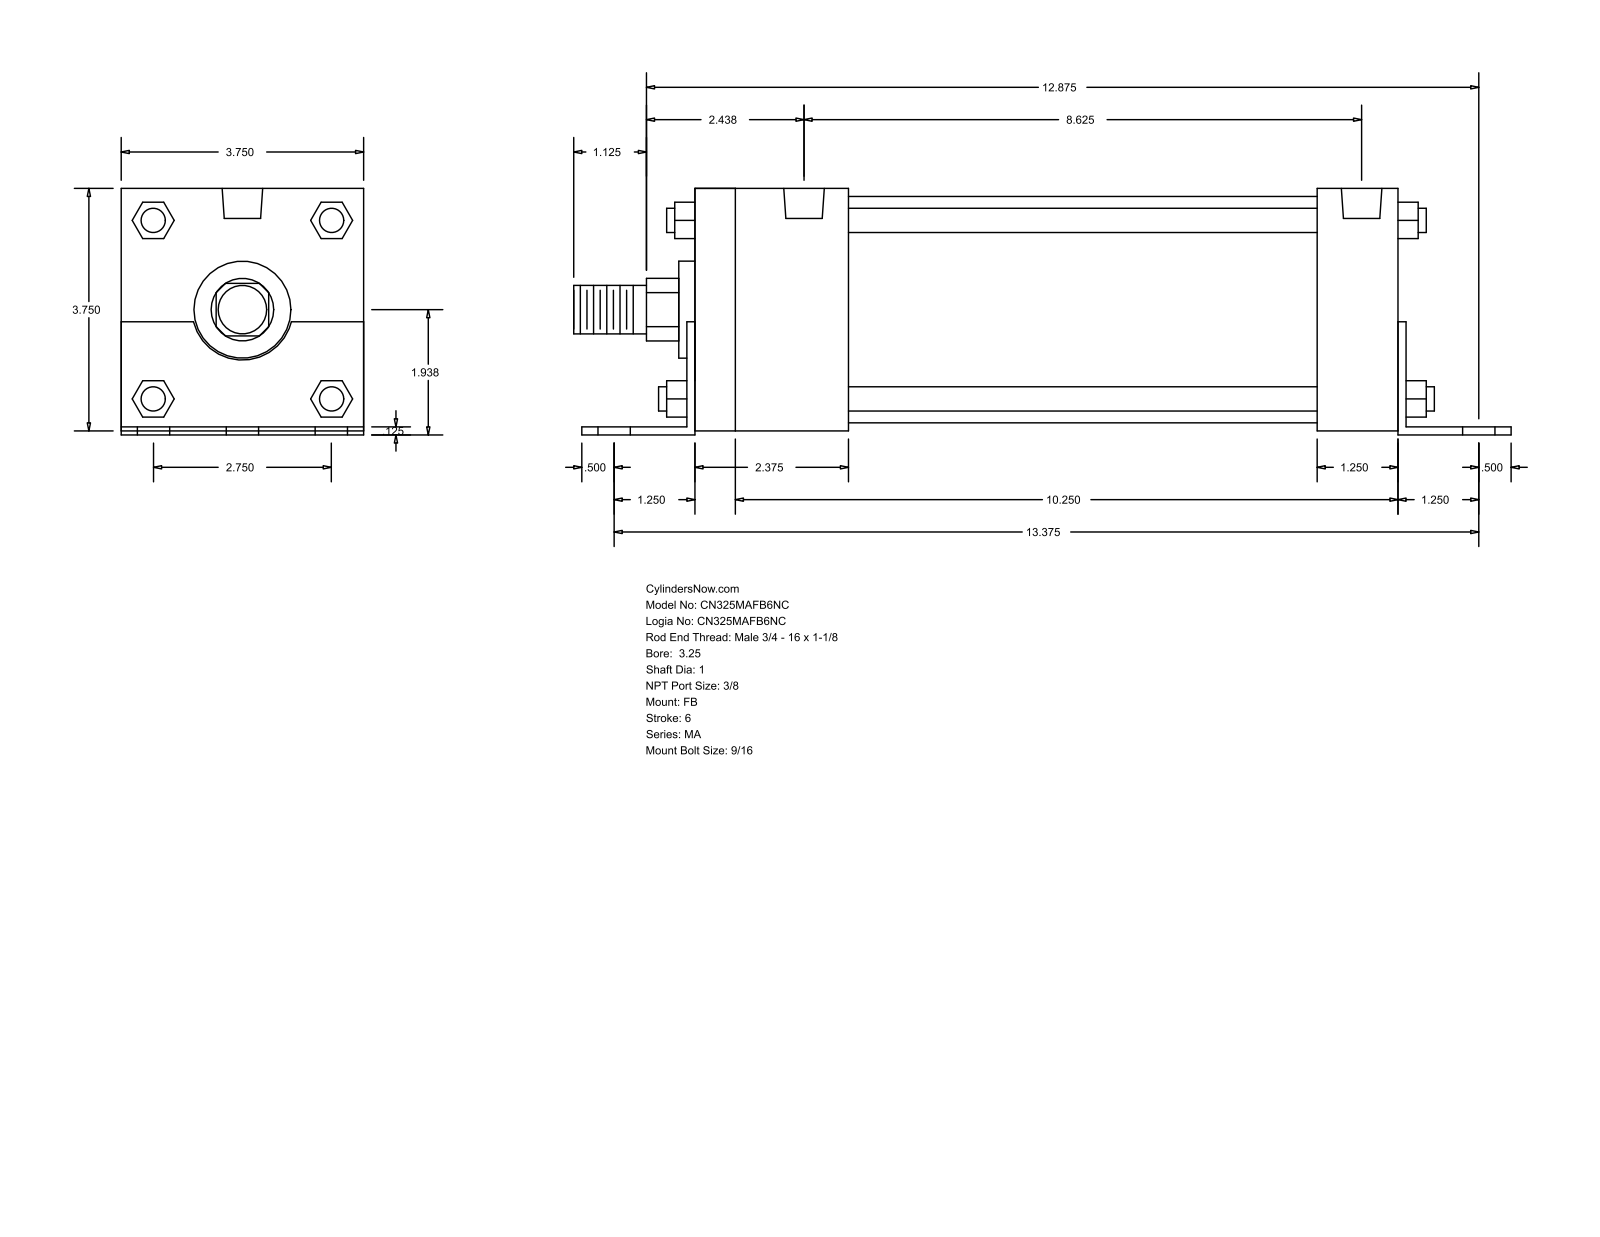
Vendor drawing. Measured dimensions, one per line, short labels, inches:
name: MA_FB__0325_1
written by: GSSL Pune (CONFIG_CONTROL_DESIGN)
unit: in
bodies: 0 solids, 140 faces (105 planar, 35 cylindrical, 0 other)
size: 14.5 × 3.813 × 3.75
holes: 6× ⌀0.563, 4× ⌀0.437, 2× ⌀0.627
bosses: 4× ⌀0.375, 1× ⌀3.5, 1× ⌀1.5, 1× ⌀1, 1× ⌀0.75
rounds: 1× R0.484, 1× R0.78
face distances: 3.75, 0.125, 0.063, 3.812, 0.062, 3.687, 0.125, 10.875, 11.125, 11
hole spacings: 1.375, 13.445, 13.375, 0.187, 2.275, 2.427, 2.75, 3.243
